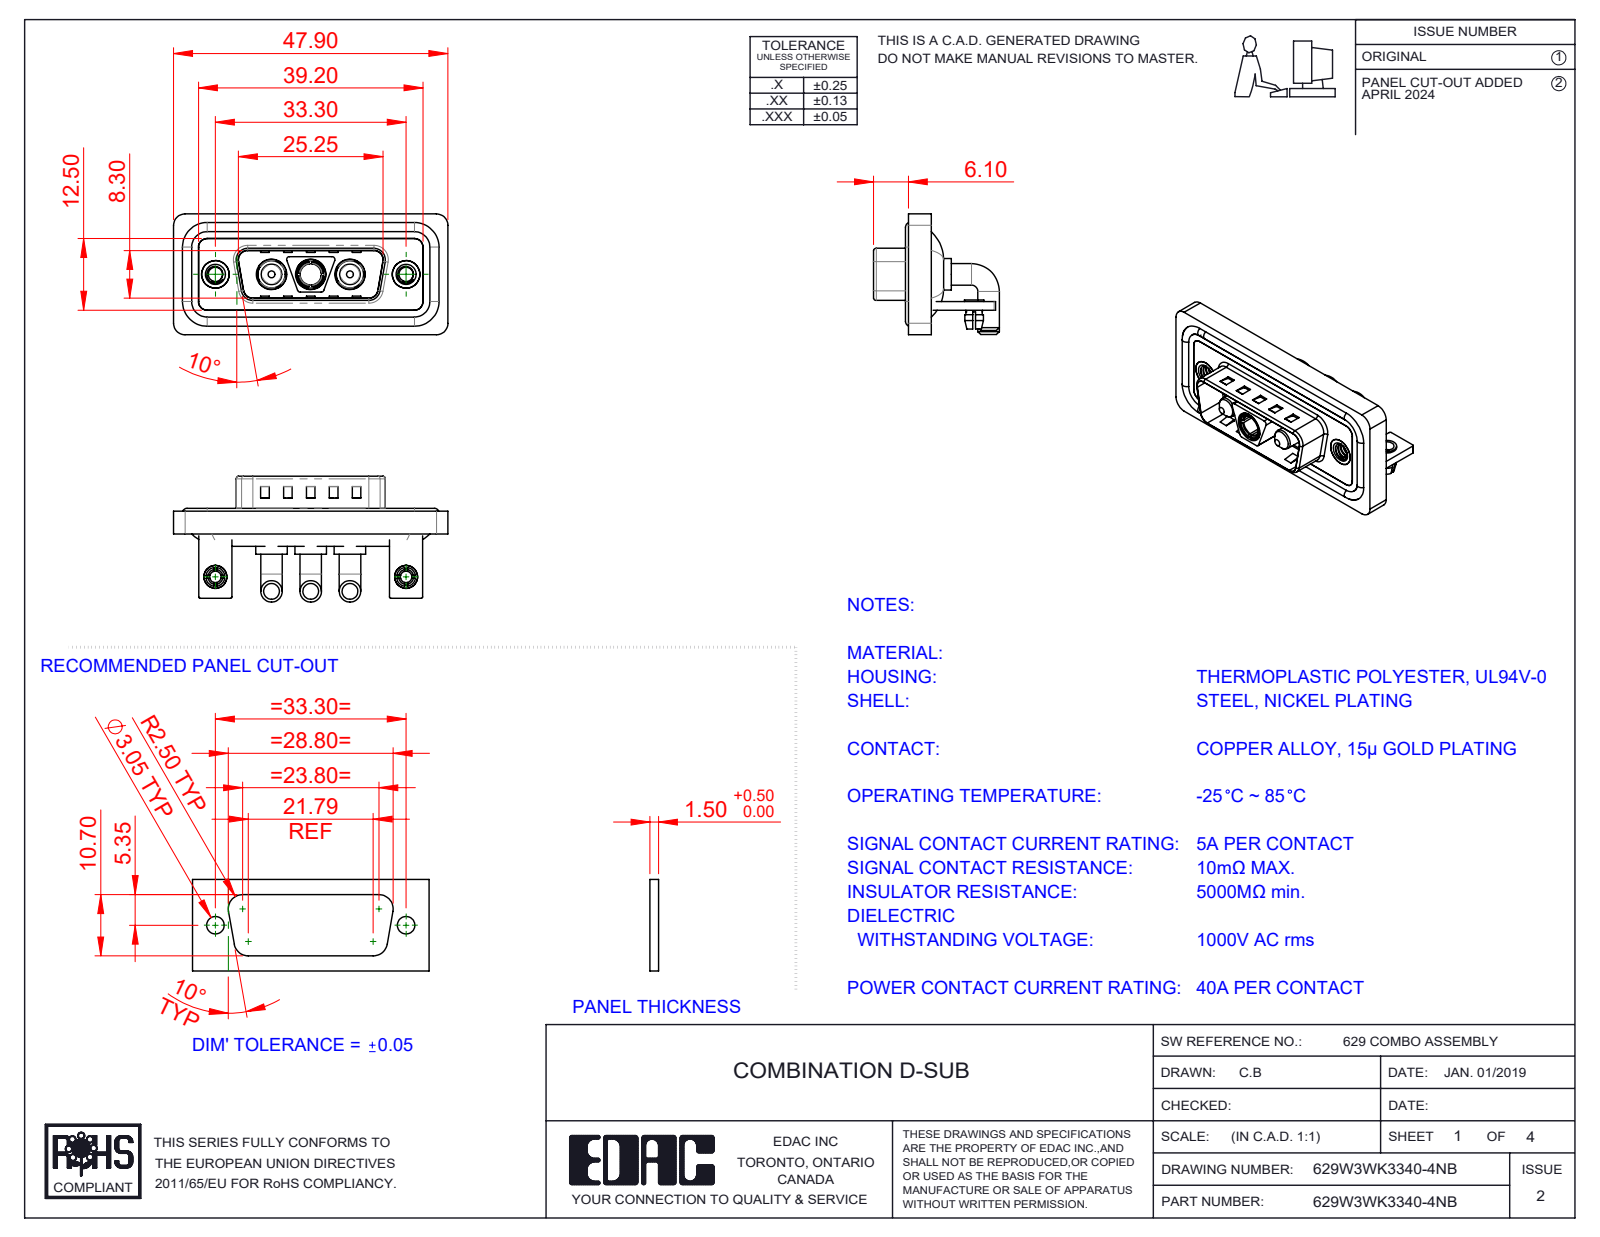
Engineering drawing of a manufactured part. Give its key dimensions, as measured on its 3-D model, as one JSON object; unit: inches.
{"part_name": "Power Socket_40A RA; 629Combo Housing_3WK3; 629W3WK3340-4NB; 629Combo Waterproof Housing_15 Contacts (+6 more)", "step_written_by": "SolidWorks 2023 (CONFIG_CONTROL_DESIGN)", "units": "inches", "bodies": {"solids": 17, "faces": 751, "planar": 299, "cylindrical": 306, "other": 146}, "overall_size": [1.886, 0.865, 0.831], "volume_in3": 0.391, "surface_area_in2": 16.04, "round_holes": [[0.098, 4], [0.191, 3], [0.209, 3], [0.079, 2], [0.126, 2], [0.157, 2], [0.189, 2], [0.197, 2], [0.146, 1]], "round_bosses_or_shafts": [[0.148, 6], [0.063, 4], [0.217, 3], [0.205, 3], [0.187, 3], [0.193, 2], [0.157, 2], [0.142, 2]], "partial_cylinders_radius": [[0.079, 21], [0.059, 18], [0.01, 16], [0.02, 13], [0.063, 8], [0.024, 4], [0.026, 4], [0.035, 4]], "face_to_face_distances": [0.016, 0.059, 0.031, 0.114, 0.043, 0.083, 0.146, 0.063, 0.047, 0.177], "hole_center_spacings": [0.27, 0.386, 0.656, 0.925, 1.311, 0.539]}
